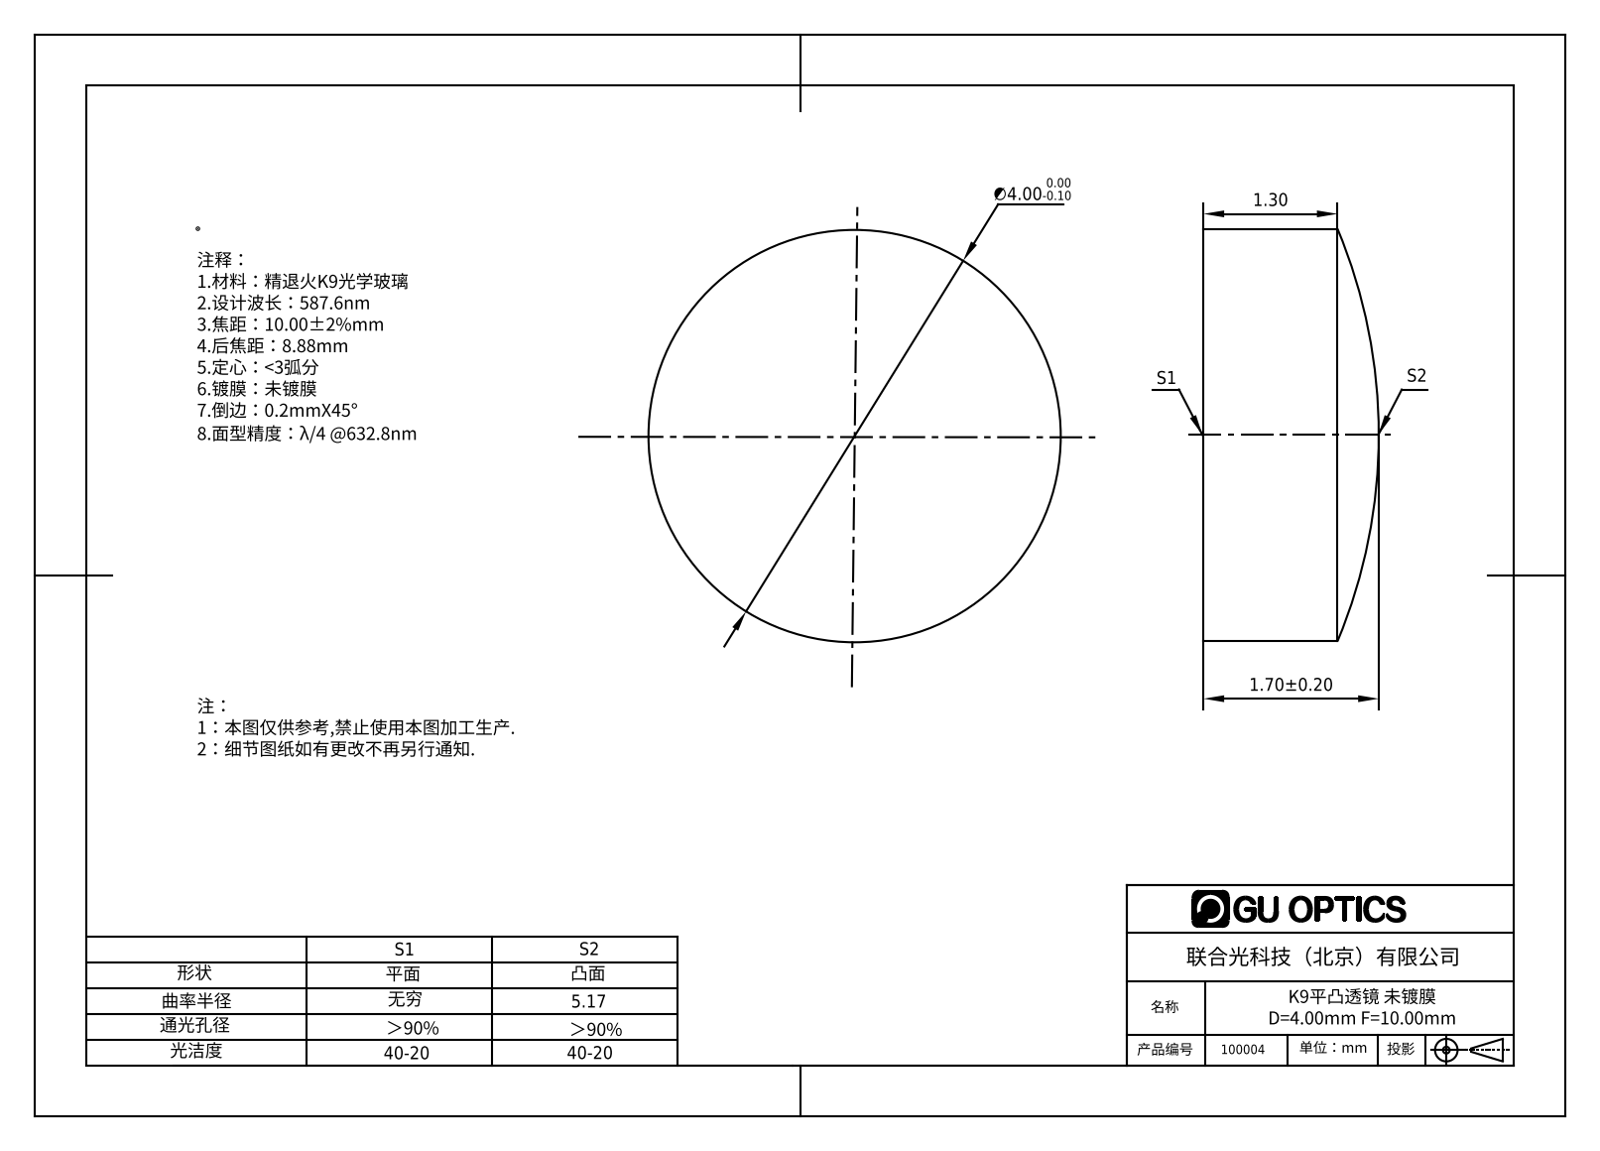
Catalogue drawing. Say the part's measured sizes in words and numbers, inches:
The part is named "100004". Its 3-D file was written by "SolidWorks 2016 (AUTOMOTIVE_DESIGN)". It is 1 solid with 5 faces: 1 planar, 2 cylindrical and 2 other. Overall it measures 0.157 by 0.157 by 0.067 inches. Its volume is 0.001 cubic inches and its surface area 0.065 square inches. Round bosses or shafts: 1 of diameter 0.157.
